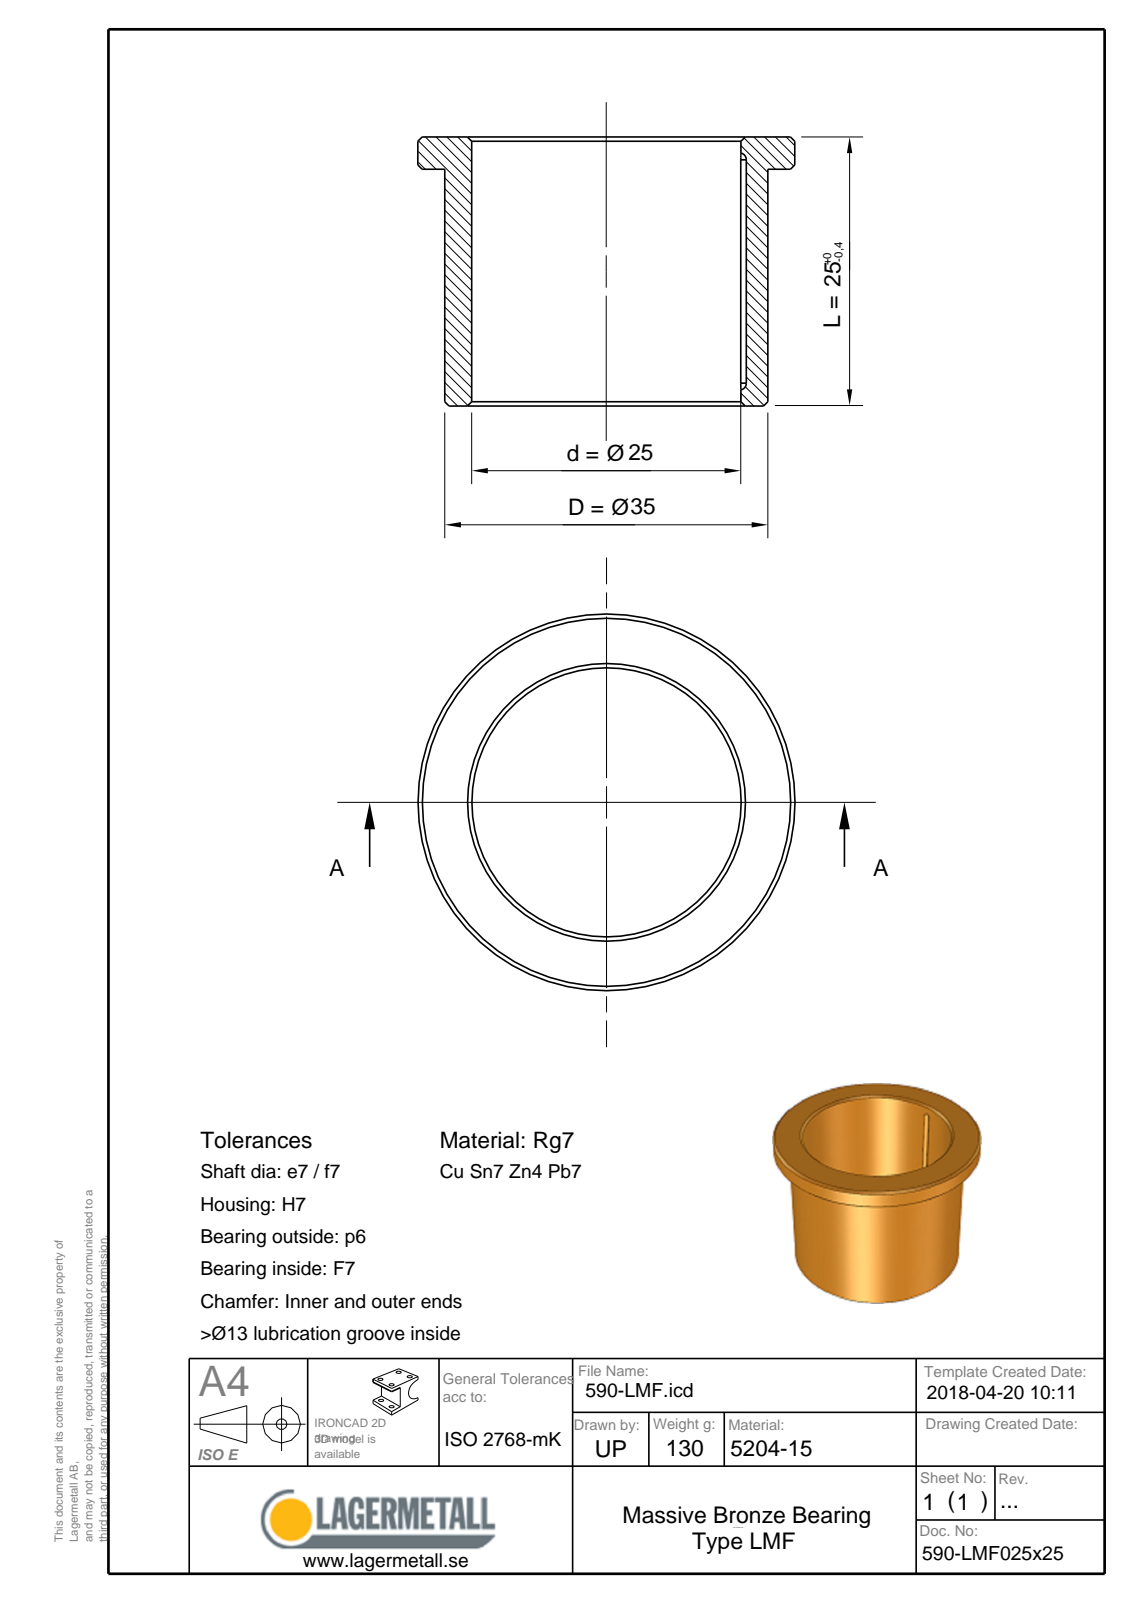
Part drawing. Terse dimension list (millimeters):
name: 590-LMF025x25
written by: Spatial InterOp 3D (CONFIG_CONTROL_DESIGN)
unit: mm
bodies: 1 solid, 16 faces (4 planar, 5 cylindrical, 7 other)
size: 45 × 45 × 25
volume: 14 822 mm³; area: 6 928 mm²
holes: 1× ⌀25
bosses: 1× ⌀45, 1× ⌀35
rounds: 2× R1.25
face distances: 5, 20, 25
